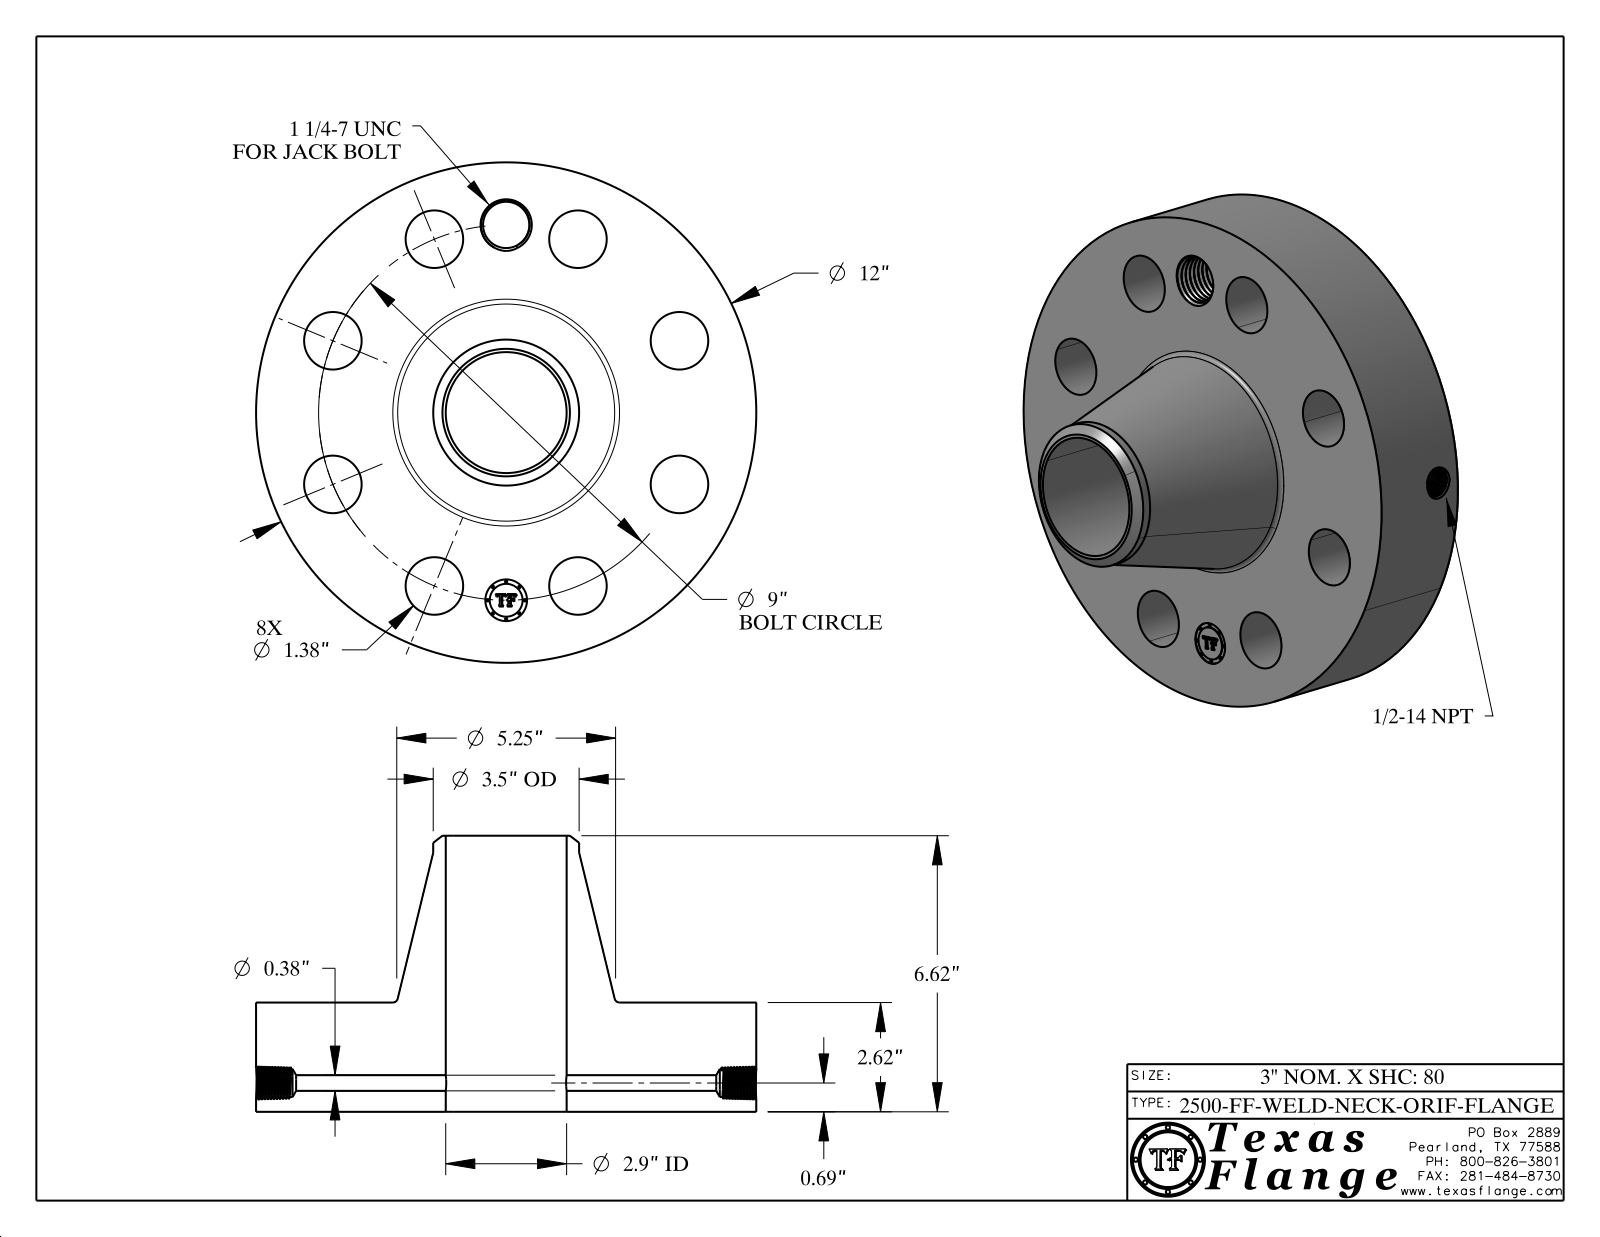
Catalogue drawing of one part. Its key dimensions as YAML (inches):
part_name: "2500-FF-WELD-NECK"
step_written_by: "CATIA V5 STEP AP214 (AUTOMOTIVE_DESIGN)"
units: inches
bodies: {solids: 1, faces: 787, planar: 368, cylindrical: 98, other: 321}
overall_size: [12, 12, 6.62]
volume: 275.3
surface_area: 507.2
round_holes:
  - {diameter: 1.38, count: 8}
  - {diameter: 0.375, count: 1}
  - {diameter: 0.672, count: 1}
  - {diameter: 1, count: 1}
  - {diameter: 1.109, count: 1}
  - {diameter: 2.9, count: 1}
round_bosses_or_shafts:
  - {diameter: 0.061, count: 8}
  - {diameter: 12, count: 1}
  - {diameter: 3.5, count: 1}
  - {diameter: 0.788, count: 1}
face_to_face_distances: [2.62, 6.62, 4, 2.605, 0.015, 4.015, 0.298, 0.293, 0.054, 0.248]
hole_center_spacings: [4.5, 3.444, 6.364, 8.315, 9, 1.756, 5, 7.483]
